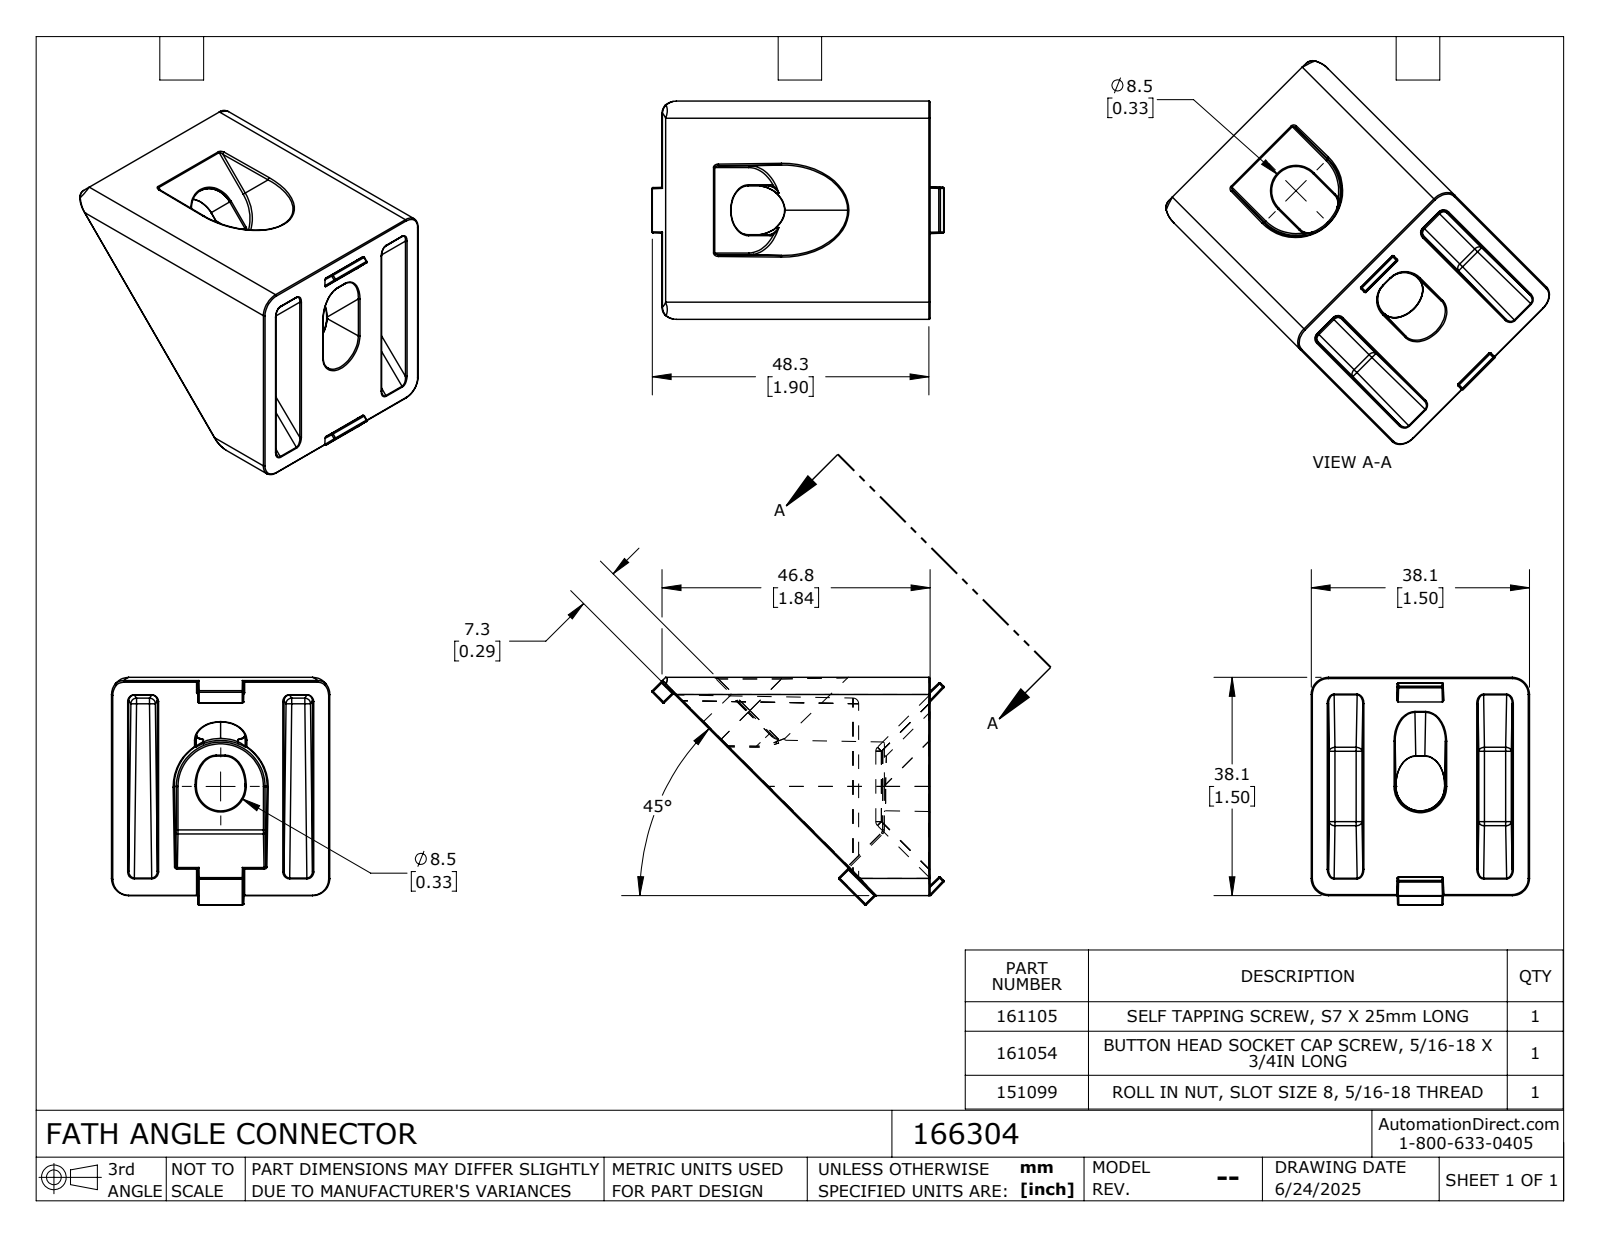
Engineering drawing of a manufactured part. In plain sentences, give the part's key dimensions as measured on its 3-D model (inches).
The part is named "166304". Its 3-D file was written by "SolidWorks 2023 (CONFIG_CONTROL_DESIGN)". It is 1 solid with 304 faces: 55 planar, 128 cylindrical and 121 other. Overall it measures 2.008 by 1.565 by 1.5 inches. Its volume is 1.598 cubic inches and its surface area 18.48 square inches. Partial cylindrical surfaces (rounded edges, fillets, slot ends): 67 of radius 0.008, 24 of radius 0.039, 9 of radius 0.012, 4 of radius 0.118, 2 of radius 0.138. The main face-to-face distances are 1.5, 1.067, 1.028, 0.096, 0.931, 0.492, 0.315, 0.177, 0.472, 0.275.
